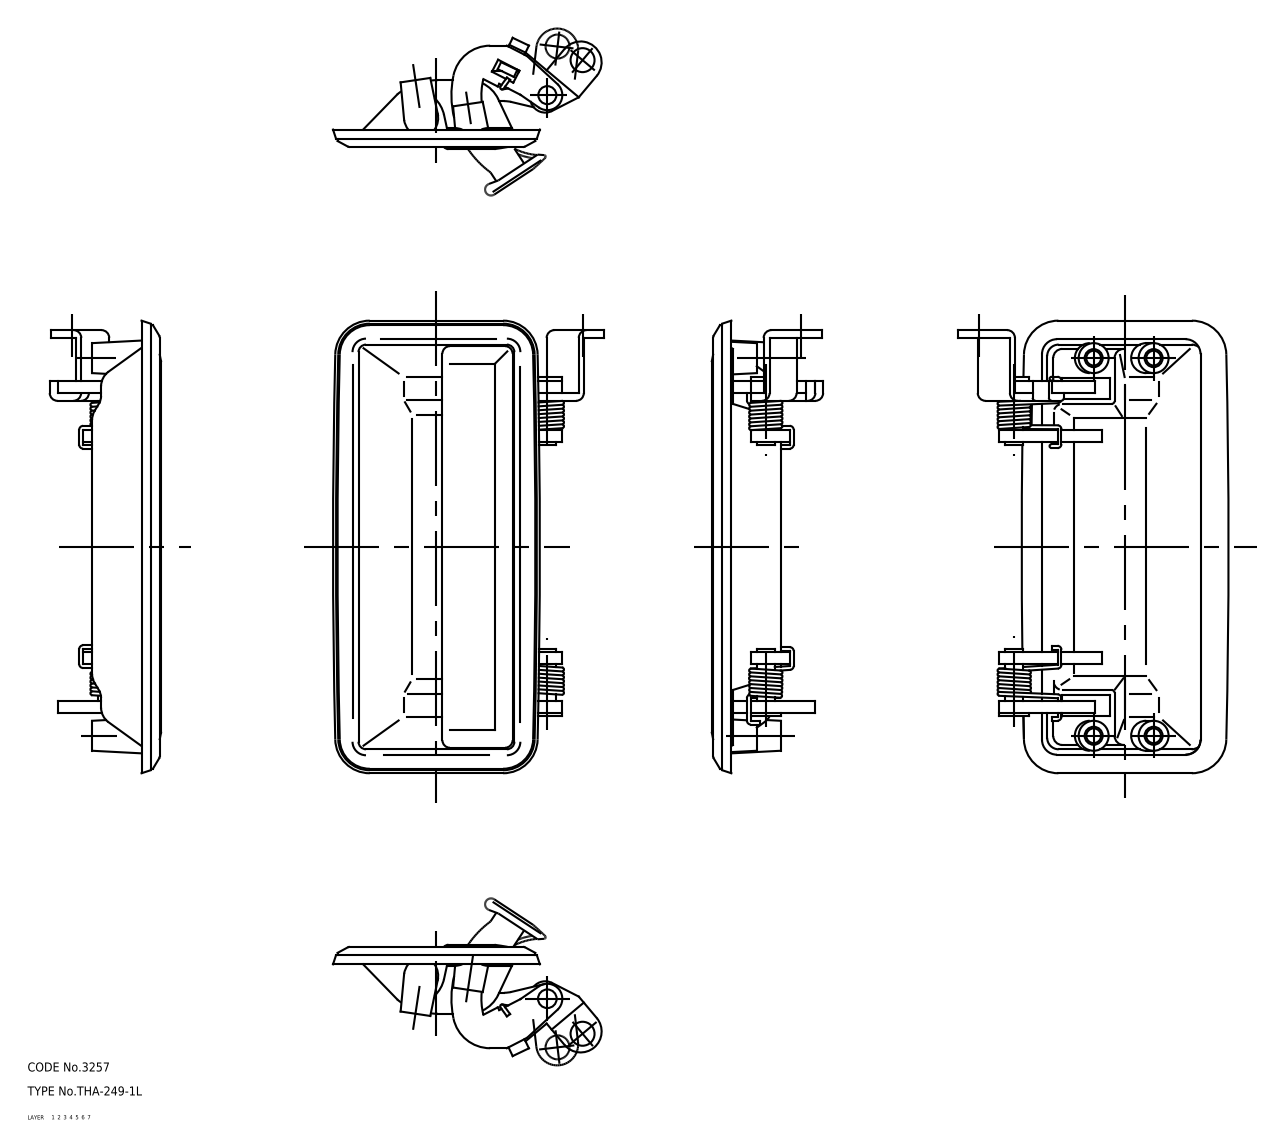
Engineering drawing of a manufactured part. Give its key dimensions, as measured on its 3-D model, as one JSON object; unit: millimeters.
{"part_name": "67151642; 67151655; 67151668; 67151681 (+4 more)", "step_written_by": "CADfix (AUTOMOTIVE_DESIGN)", "units": "millimeters", "bodies": {"solids": 8, "faces": 494, "planar": 0, "cylindrical": 0, "other": 494}, "overall_size": [151, 89.61, 37.12], "volume_mm3": 55942, "surface_area_mm2": 53516}
